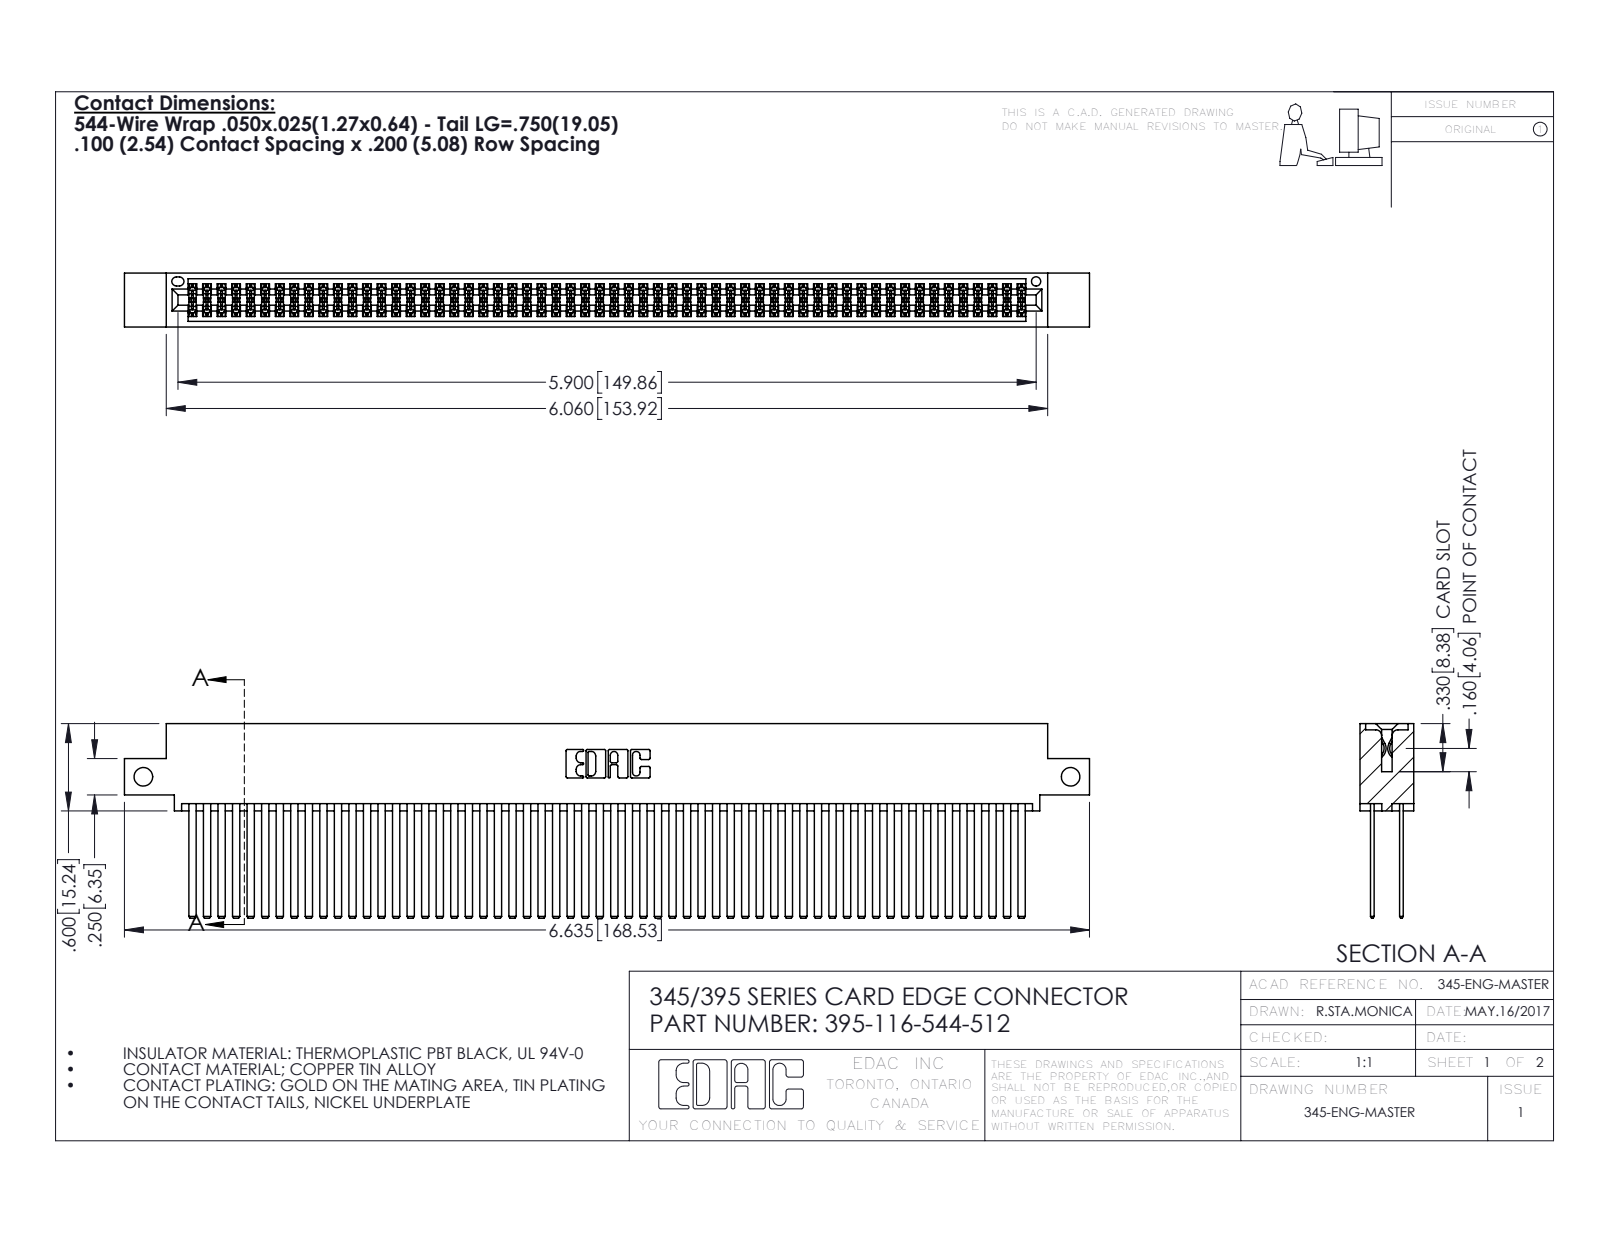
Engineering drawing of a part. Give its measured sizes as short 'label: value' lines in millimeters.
name: 345 Part_0.110 Offset - Side Mount; 345-292-001_345-293-144; 395-116-544-512
written by: SolidWorks 2016 (CONFIG_CONTROL_DESIGN)
unit: mm
bodies: 117 solids, 5234 faces (3448 planar, 1786 cylindrical, 0 other)
size: 168.5 × 34 × 9.4
volume: 17 990 mm³; area: 31 620 mm²
holes: 2× ⌀3.3, 1× ⌀1.6
rounds: 174× R0.2, 22× R0.3, 6× R0.2, 6× R0.8, 3× R0.7, 2× R0.4, 2× R0.5, 2× R0.6
face distances: 5.1, 0.6, 7.6, 1.8, 2.5, 6.9, 5.7, 4.4, 9.4, 1.3
hole spacings: 161.9
